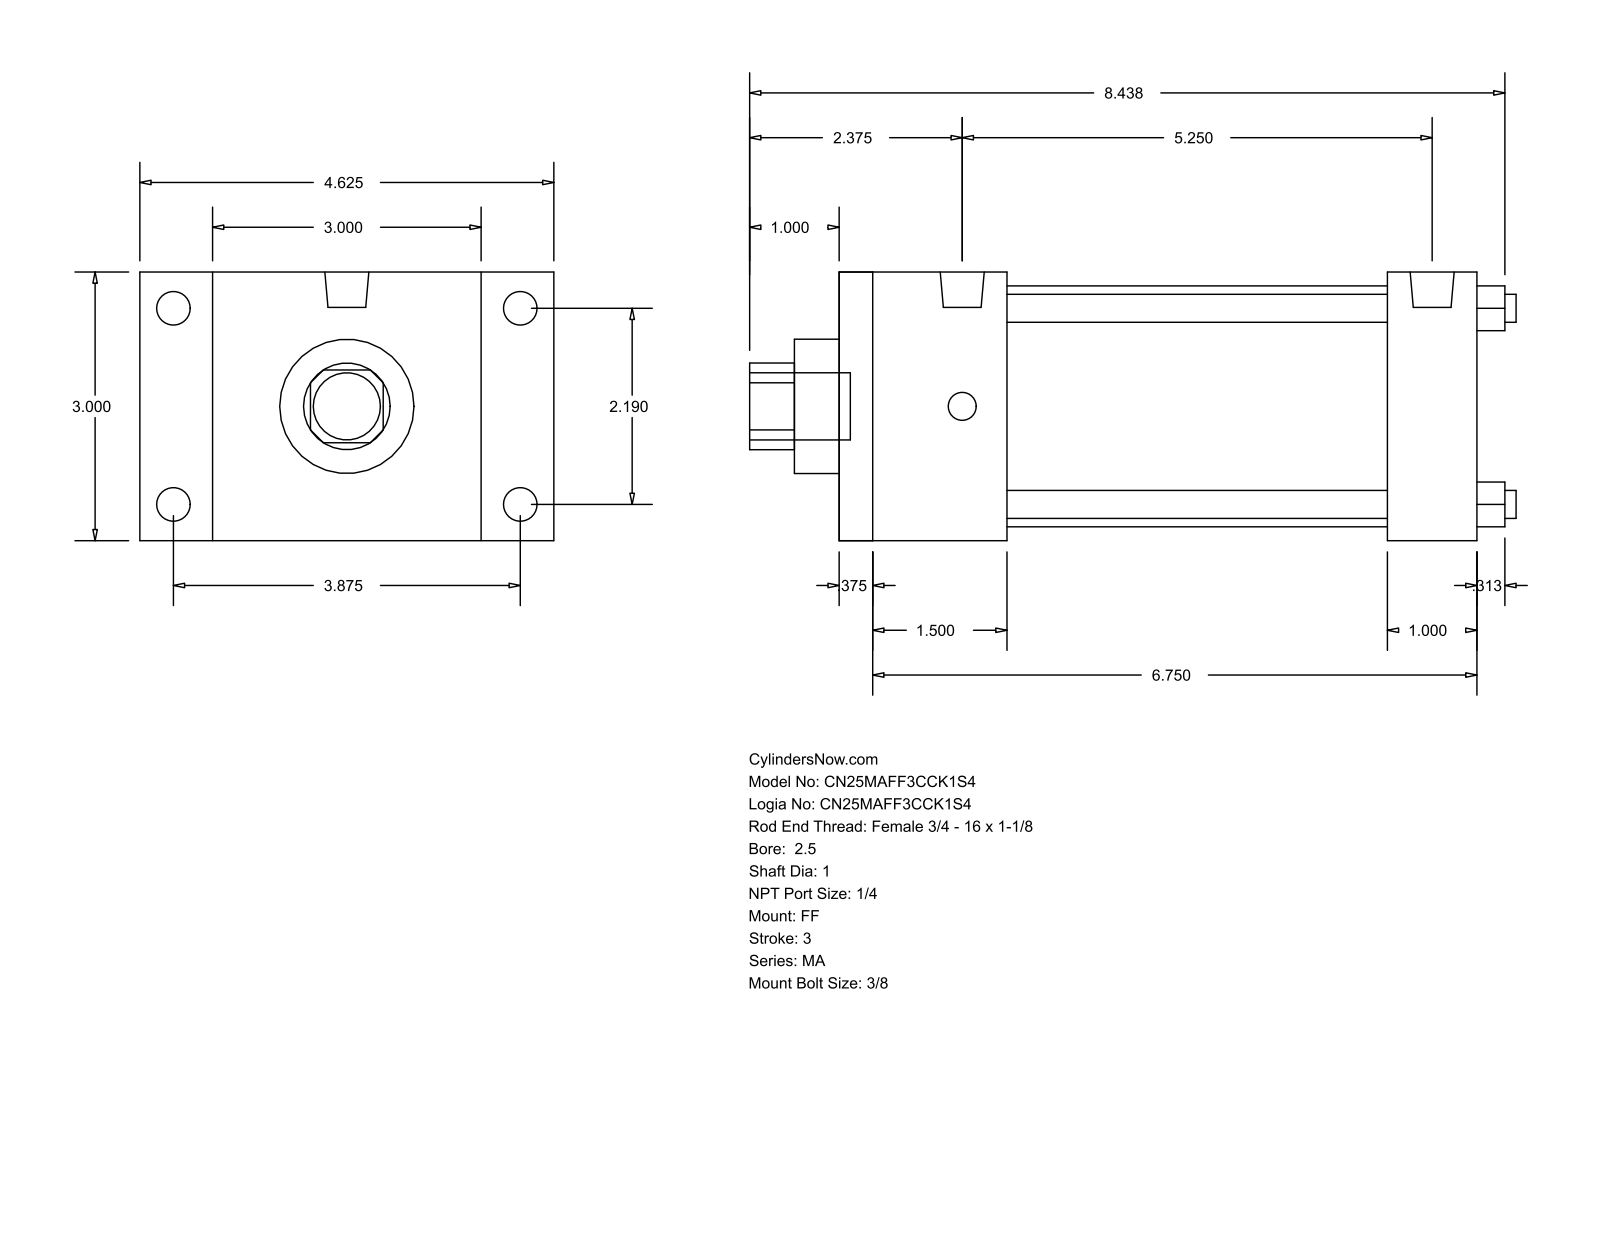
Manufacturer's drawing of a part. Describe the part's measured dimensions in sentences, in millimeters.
The part is named "MA_FF__0250_1". Its 3-D file was written by "GSSL Pune (CONFIG_CONTROL_DESIGN)". It is 0 solids with 92 faces: 64 planar, 28 cylindrical and 0 other. Overall it measures 217.49 by 117.47 by 76.2 millimeters. Round holes: 4 of diameter 7.94, 1 of diameter 25.4, 1 of diameter 38.1, 1 of diameter 68.33. Round bosses or shafts: 4 of diameter 9.53, 4 of diameter 7.94, 2 of diameter 12.49, 1 of diameter 19.05. Partial cylindrical surfaces (rounded edges, fillets, slot ends): 1 of radius 12.29. The main face-to-face distances are 76.2, 180.98, 9.52, 171.46, 47.63, 155.57, 38.11, 146.05, 107.94, 133.35. The hole center spacings are 39.33, 55.62, 78.66.
